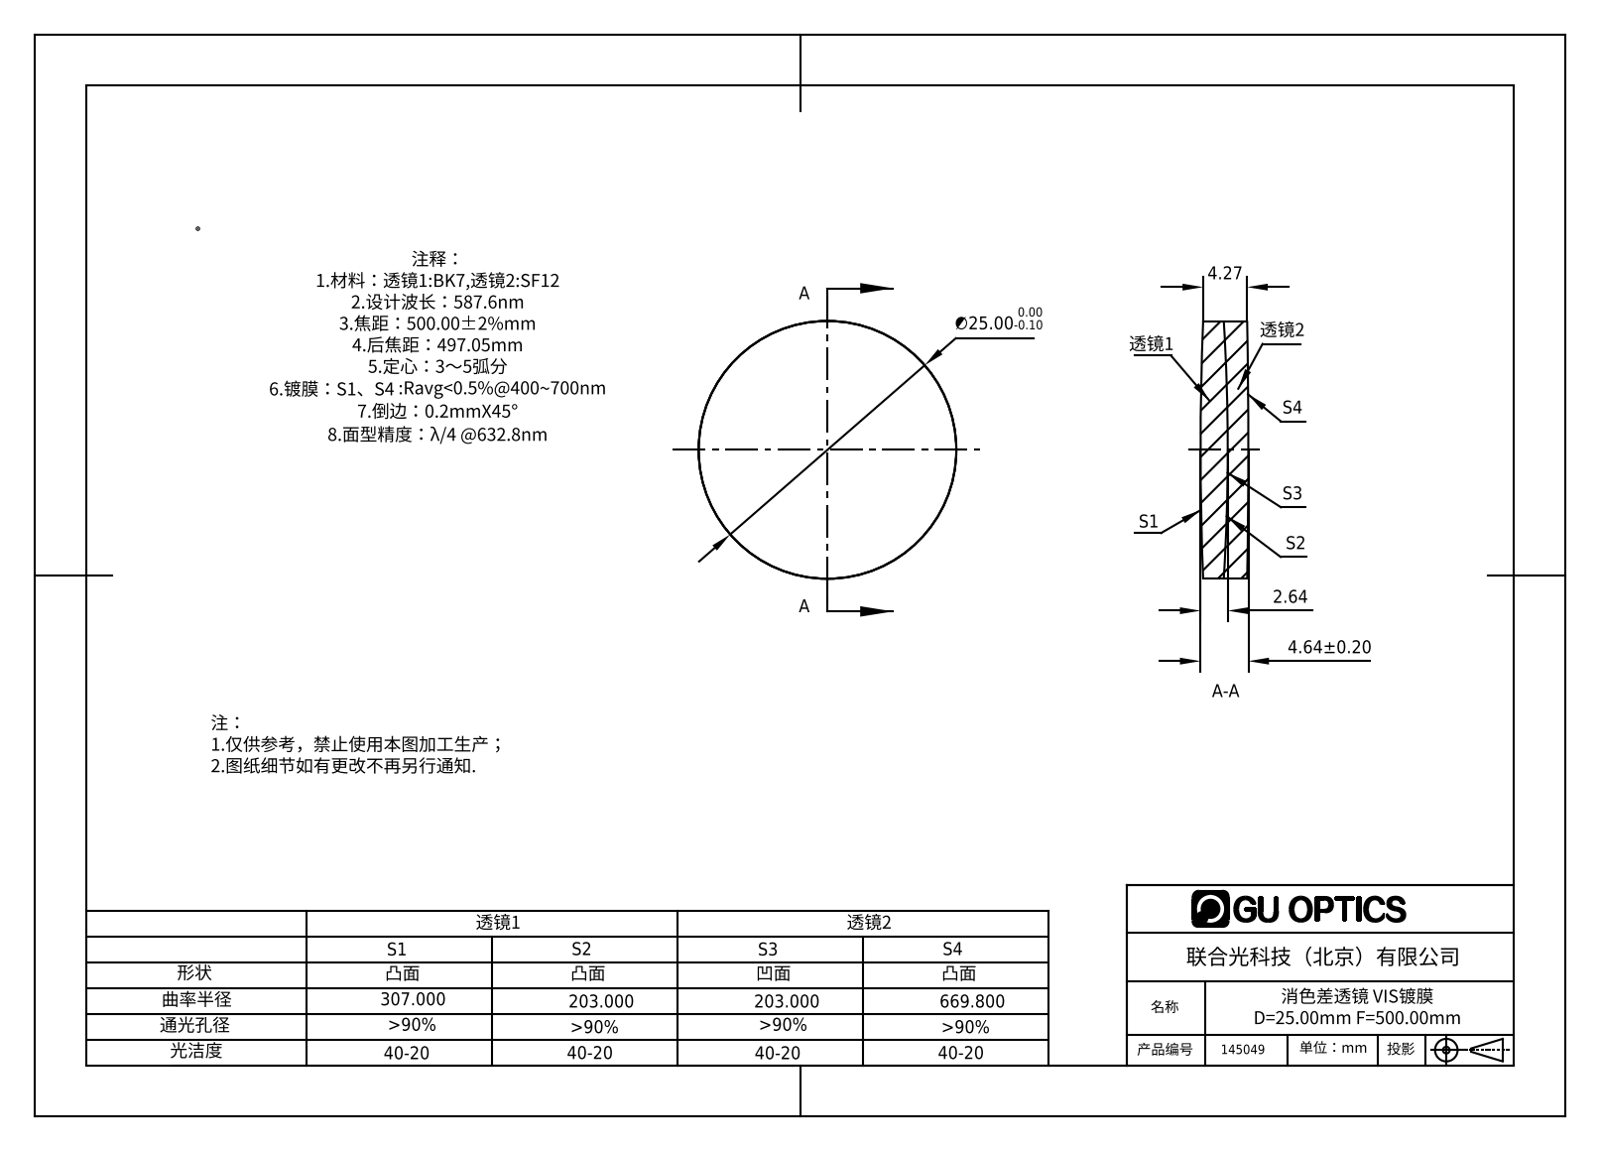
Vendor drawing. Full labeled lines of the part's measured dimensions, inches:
Part name (STEP PRODUCT): 145049
STEP written by: SolidWorks 2016 (AUTOMOTIVE_DESIGN)
Units: inches
Bodies: 2 solids, 12 faces (0 planar, 4 cylindrical, 8 other)
Overall size (bounding box): 0.984 × 0.984 × 0.183
Volume: 0.133 in³ · Surface area: 3.565 in²
Round bosses / shafts (diameter × count): ⌀0.984 ×1
